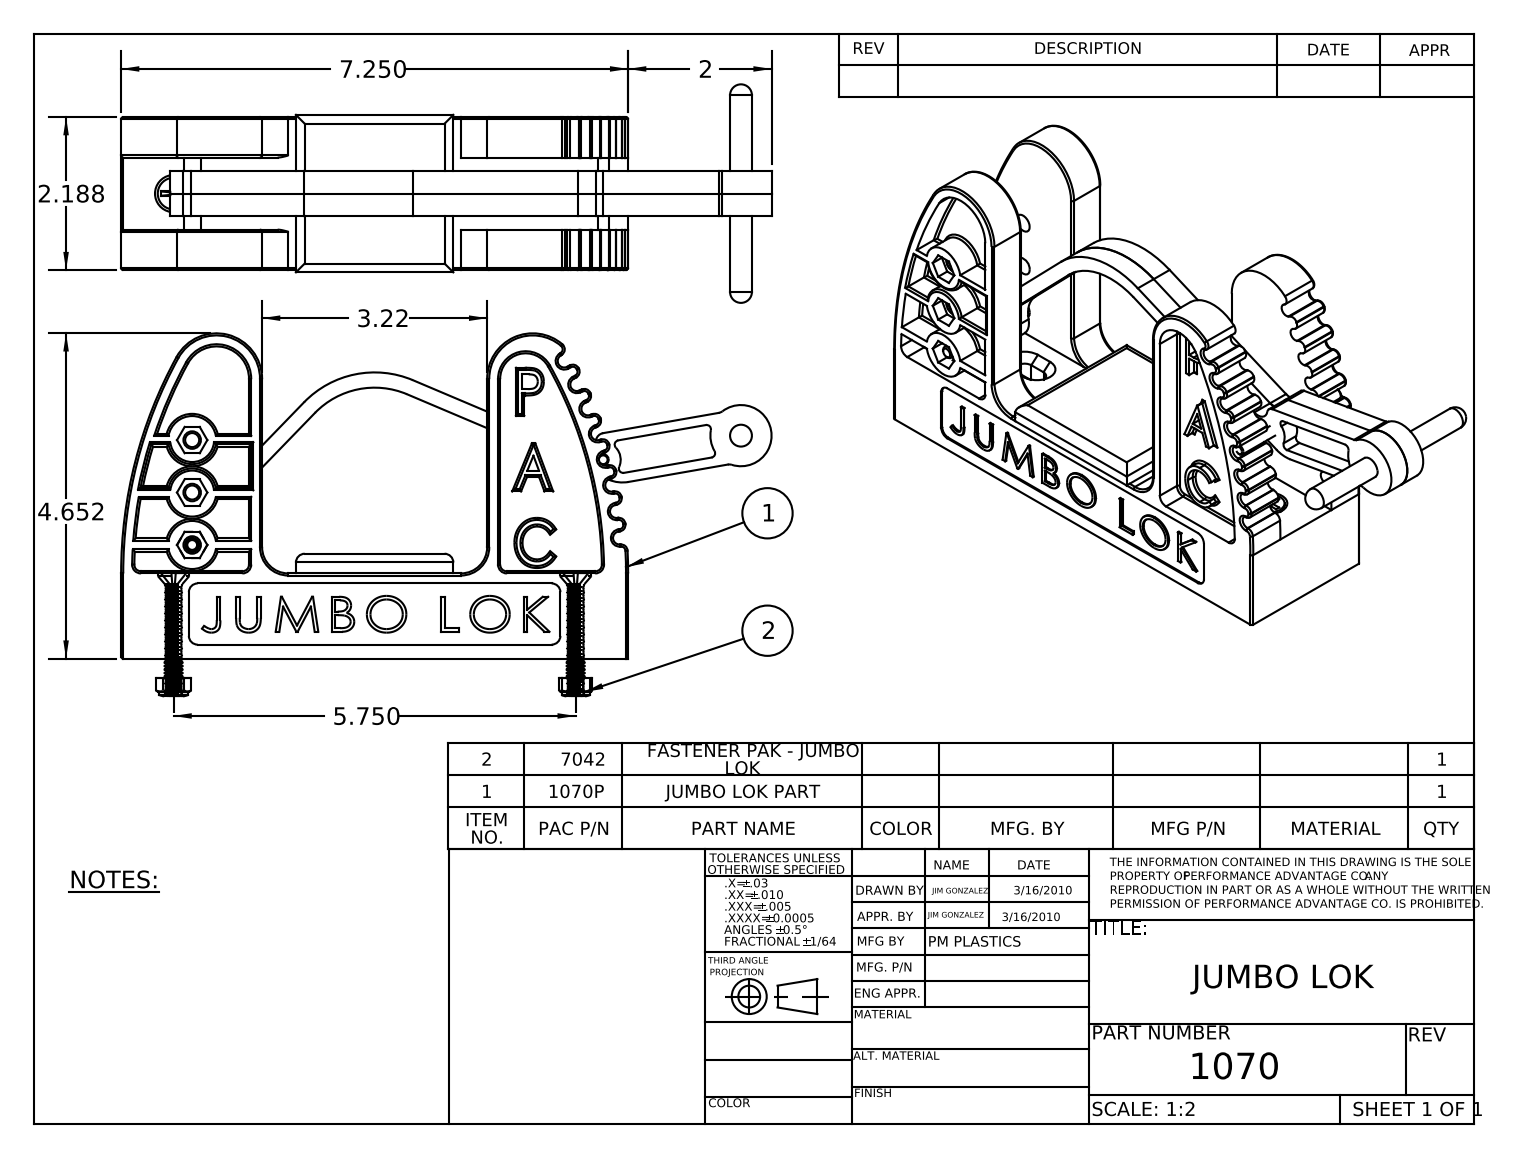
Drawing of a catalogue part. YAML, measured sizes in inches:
part_name: "1070 #10-24 Nut_MSHXNUT 0.250-20-S-N; 1070 Shoulder Screw_SHSSCREW 0.25x1.25-N; 1070P; 1070 Base (+2 more)"
step_written_by: "SolidWorks 2010 (CONFIG_CONTROL_DESIGN)"
units: inches
bodies: {solids: 10, faces: 1324, planar: 489, cylindrical: 429, other: 406}
overall_size: [9.301, 4.652, 3.125]
volume: 20.68
surface_area: 235
round_holes:
  - {diameter: 0.266, count: 5}
  - {diameter: 0.25, count: 4}
  - {diameter: 0.201, count: 3}
  - {diameter: 0.437, count: 3}
  - {diameter: 0.156, count: 1}
  - {diameter: 0.313, count: 1}
round_bosses_or_shafts:
  - {diameter: 0.23, count: 4}
  - {diameter: 0.2, count: 4}
  - {diameter: 0.687, count: 3}
  - {diameter: 0.641, count: 2}
  - {diameter: 0.375, count: 1}
  - {diameter: 0.248, count: 1}
  - {diameter: 0.227, count: 1}
  - {diameter: 0.19, count: 1}
partial_cylinders:
  - {radius: 0.03, count: 103}
  - {radius: 0.094, count: 16}
  - {radius: 0.125, count: 15}
  - {radius: 0.031, count: 8}
  - {radius: 0.094, count: 8}
  - {radius: 0.375, count: 5}
  - {radius: 0.062, count: 4}
  - {radius: 0.133, count: 4}
face_to_face_distances: [0.187, 1, 1.813, 0.813, 0.578, 1.609, 0.516, 0.906, 1.094, 2]
hole_center_spacings: [8.002, 0.75, 0.75, 0.75, 1.5, 1.5, 2, 5.75]
